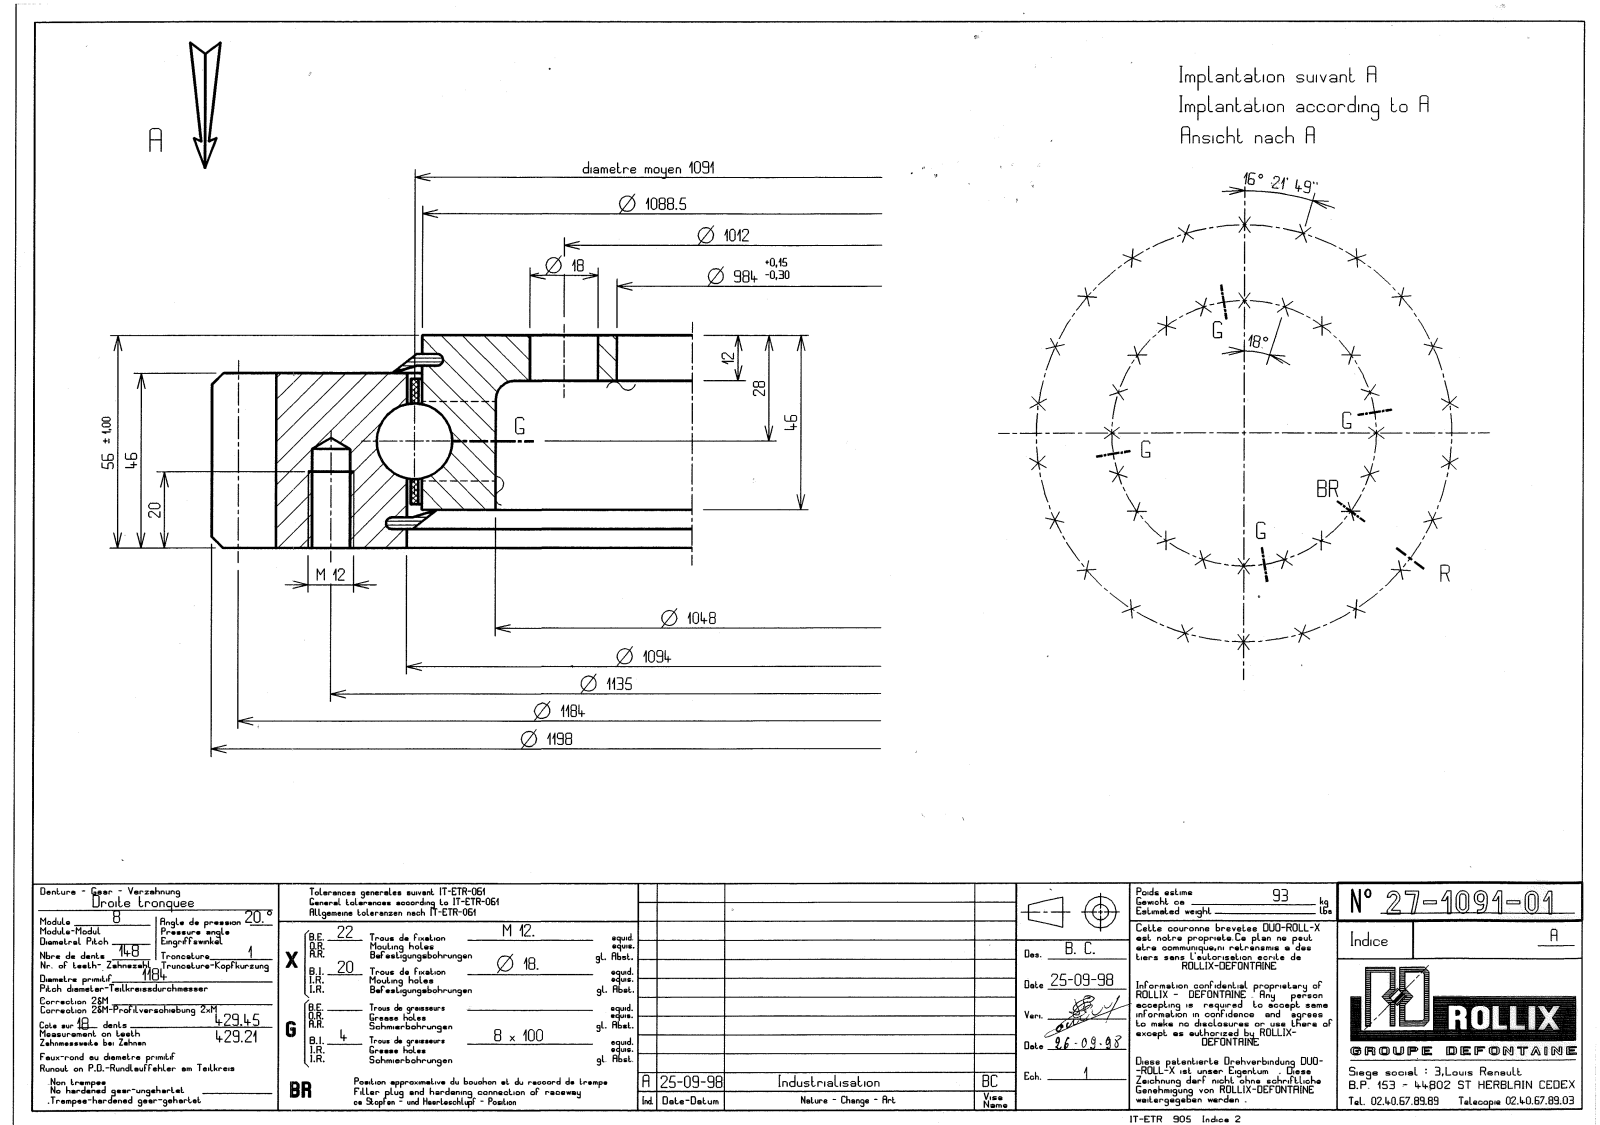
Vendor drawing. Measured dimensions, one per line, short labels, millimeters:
name: 21-1091-01
written by: SolidWorks 2016 (CONFIG_CONTROL_DESIGN)
unit: mm
bodies: 9 solids, 1172 faces (349 planar, 413 cylindrical, 410 other)
size: 1197.87 × 1197.87 × 56
volume: 10 640 000 mm³; area: 1 770 000 mm²
holes: 22× ⌀10.25, 20× ⌀18, 4× ⌀7, 1× ⌀984, 1× ⌀1048, 1× ⌀1095.5
bosses: 4× ⌀8, 1× ⌀1086.5
rounds: 1× R582, 1× R599
face distances: 10, 46, 56, 44, 2, 12, 34, 36, 8.05, 47.95
hole spacings: 567.5, 613.63, 743.27, 857.77, 1032.43, 319.76, 471.5, 1089.02
